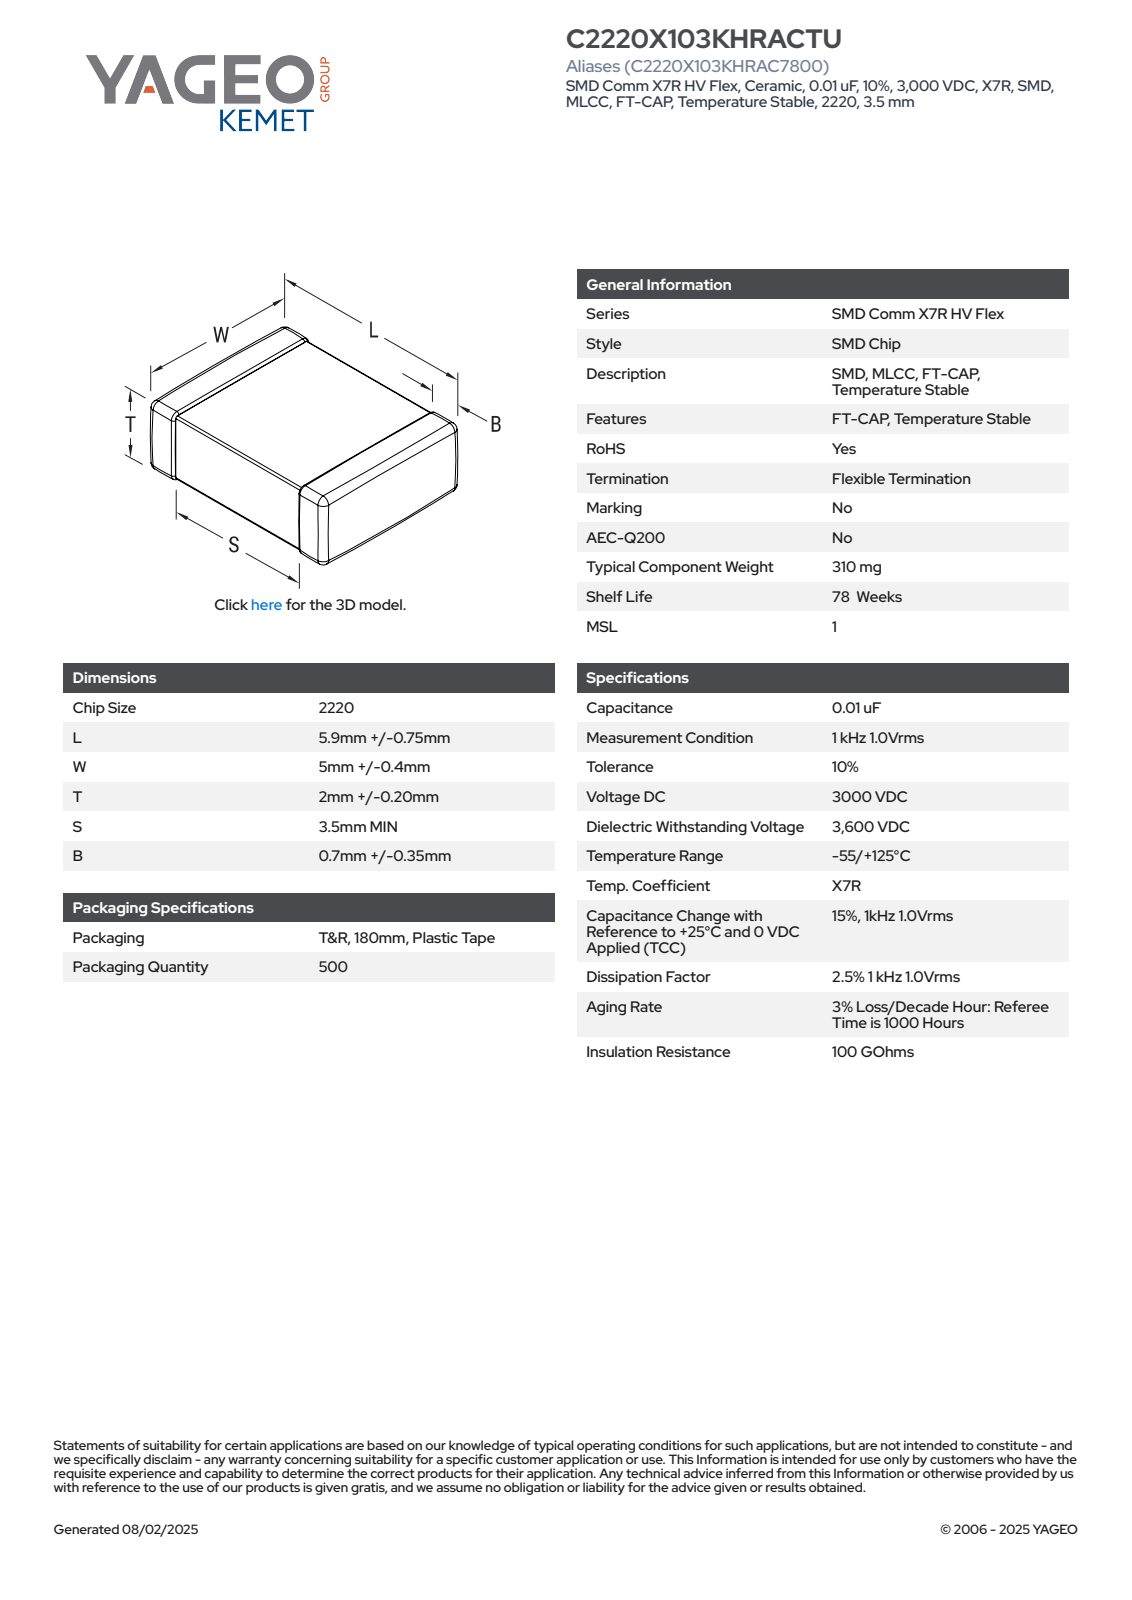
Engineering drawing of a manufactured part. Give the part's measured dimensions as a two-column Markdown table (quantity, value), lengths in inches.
| quantity | value |
| --- | --- |
| part name | CCS_CCSTD_2220_L6.65W5.4T2.2B0.7 |
| STEP written by | SolidWorks 2021 (AUTOMOTIVE_DESIGN) |
| units | inches |
| bodies | 4 solids, 121 faces (71 planar, 34 cylindrical, 16 other) |
| overall size | 0.262 × 0.213 × 0.087 |
| volume | 0.004 in³ |
| surface area | 0.192 in² |
| partial cylindrical surfaces (radius × count) | 0.004 × 24 |
| main face-to-face distances | 0.078, 0.082, 0.262, 0.087, 0.204, 0.208, 0.213, 0.11, 0.152, 0.141 |
